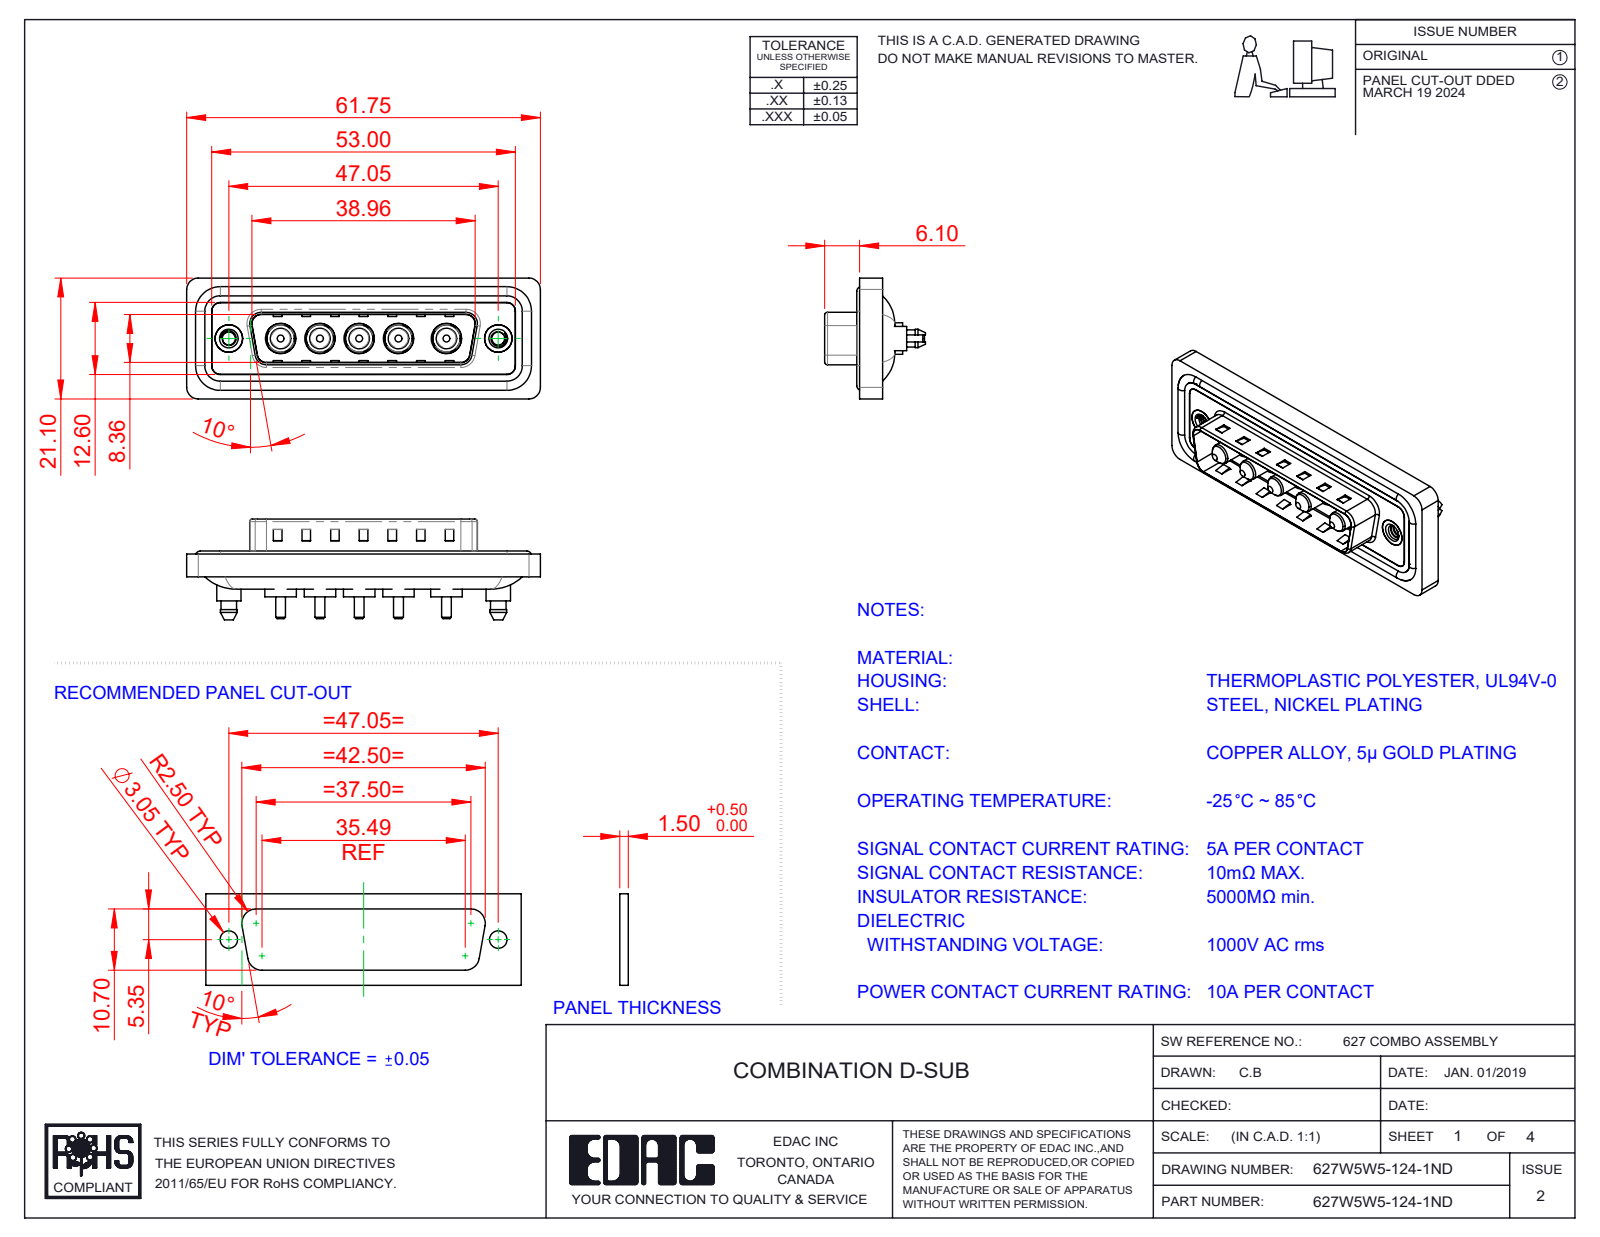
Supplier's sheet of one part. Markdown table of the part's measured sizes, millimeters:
| quantity | value |
| --- | --- |
| part name | 627Combo Threaded Boardlock_5; 627Combo Shell Front_25 Contacts; 627Combo Waterproof Housing_25 Contacts; 627Combo Threaded Boardlock_D (+4 more) |
| STEP written by | SolidWorks 2023 (CONFIG_CONTROL_DESIGN) |
| units | millimeters |
| bodies | 17 solids, 736 faces (275 planar, 323 cylindrical, 138 other) |
| overall size | 61.75 × 21.1 × 17.6 |
| volume | 7 534 mm³ |
| surface area | 12 069 mm² |
| round holes (diameter × count) | 4.85 × 5, 5.3 × 5, 2.26 × 2, 4 × 2, 4.8 × 2, 5 × 2 |
| round bosses / shafts (diameter × count) | 5.5 × 5, 5.2 × 5, 4.75 × 5, 3.75 × 5, 3.6 × 5, 1.7 × 5, 1.6 × 4, 5.4 × 2 |
| partial cylindrical surfaces (radius × count) | 1.5 × 24, 2 × 18, 1.6 × 10, 0.5 × 8, 2.1 × 5, 0.25 × 4, 0.6 × 4, 0.65 × 4 |
| main face-to-face distances | 0.4, 1.5, 1.1, 0.5, 3.1, 1.6, 2.9, 0.82, 9.58, 5.65 |
| hole center spacings | 6.86, 9.04, 13.73, 38.01, 6.87, 8.37, 8.38, 9.05 |
